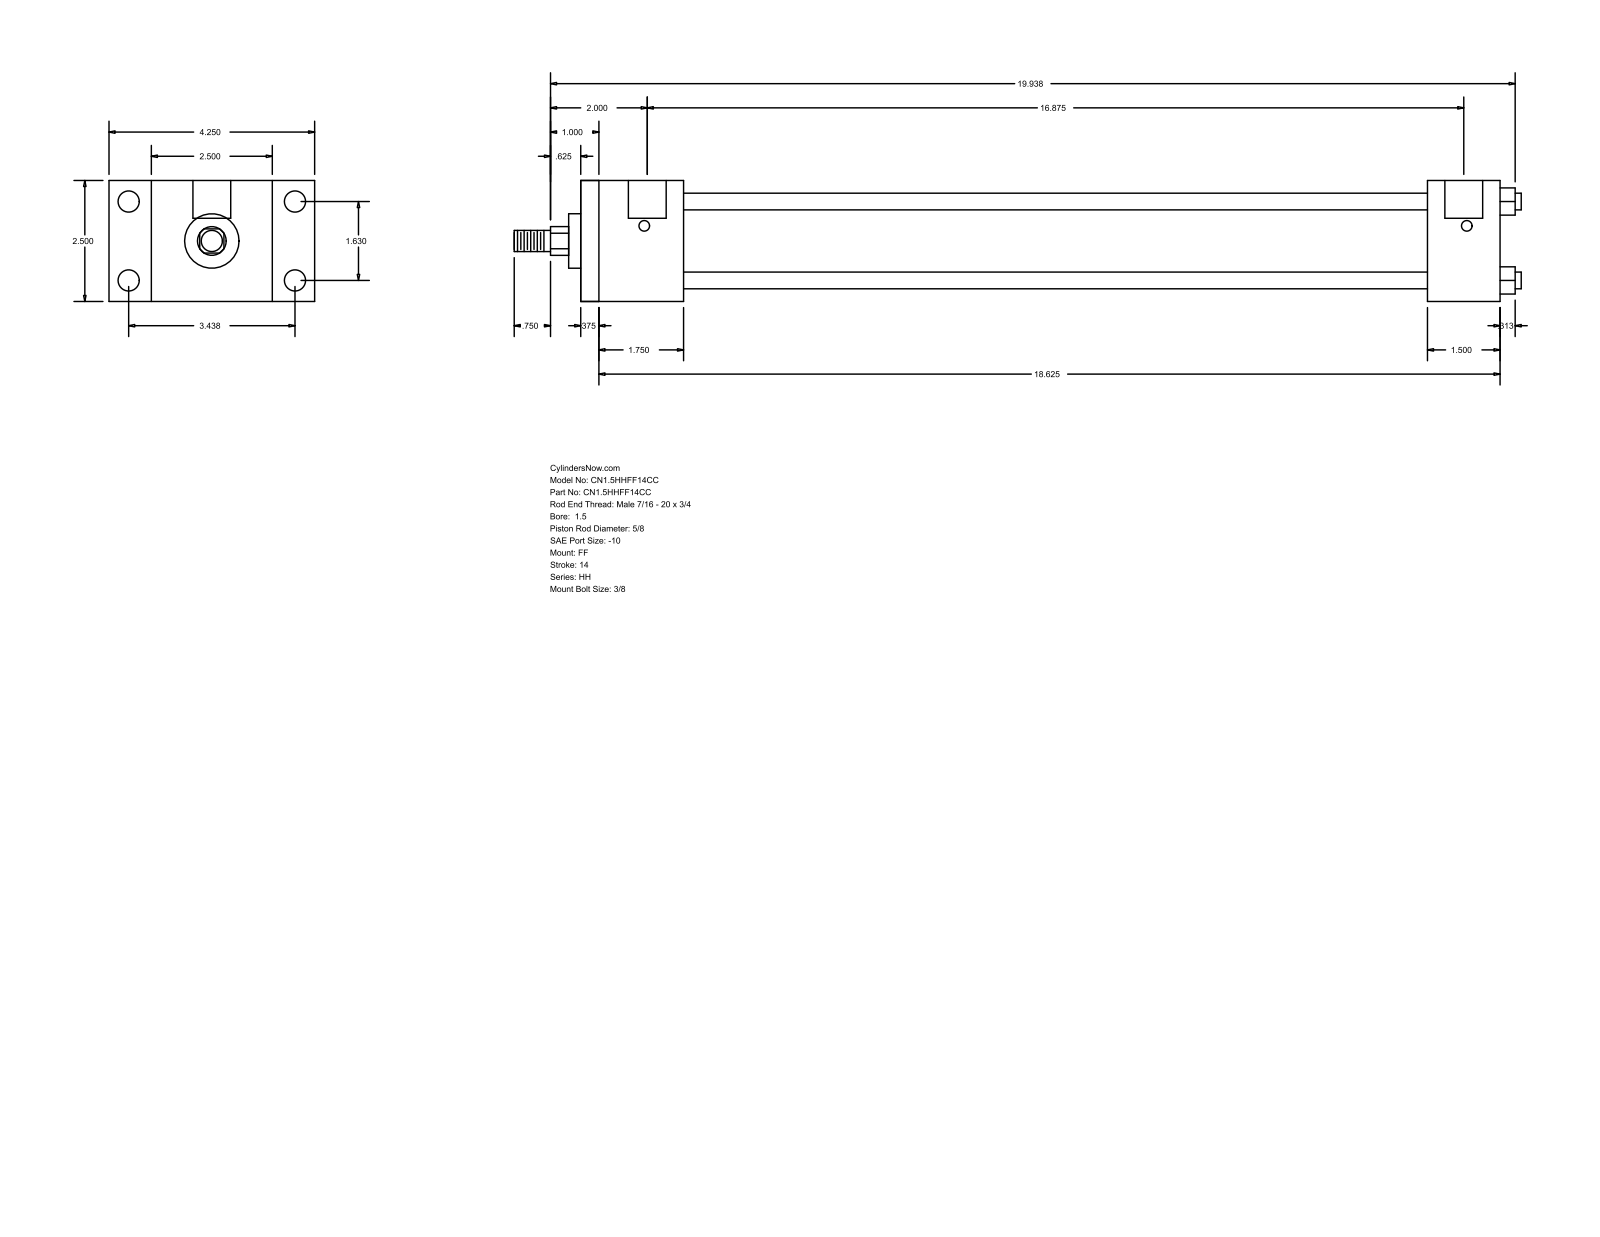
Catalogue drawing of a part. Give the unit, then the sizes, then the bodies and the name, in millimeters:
Units: millimetres
Overall size (bounding box): 528.64 × 107.95 × 63.5
Round holes (diameter × count): ⌀5.56 ×4, ⌀11.13 ×4, ⌀19.84 ×2
Round bosses / shafts (diameter × count): ⌀8.76 ×4, ⌀44.45 ×1, ⌀28.57 ×1, ⌀15.88 ×1, ⌀11.11 ×1
Partial cylindrical surfaces — rounded edges, fillets, slot ends (radius × count): R7.54 ×1
Main face-to-face distances: 63.5, 482.6, 38.1, 9.52, 473.08, 44.45, 53.97, 428.63, 444.5, 434.98
Hole centre spacings: 41.4, 87.32, 96.64, 431.8, 1.58, 1.59, 428.63, 430.21
Bodies: 0 solids, 92 faces (64 planar, 28 cylindrical, 0 other)
Part name (STEP PRODUCT): HH_FF__0150_0.625
STEP written by: GSSL Pune (CONFIG_CONTROL_DESIGN)
